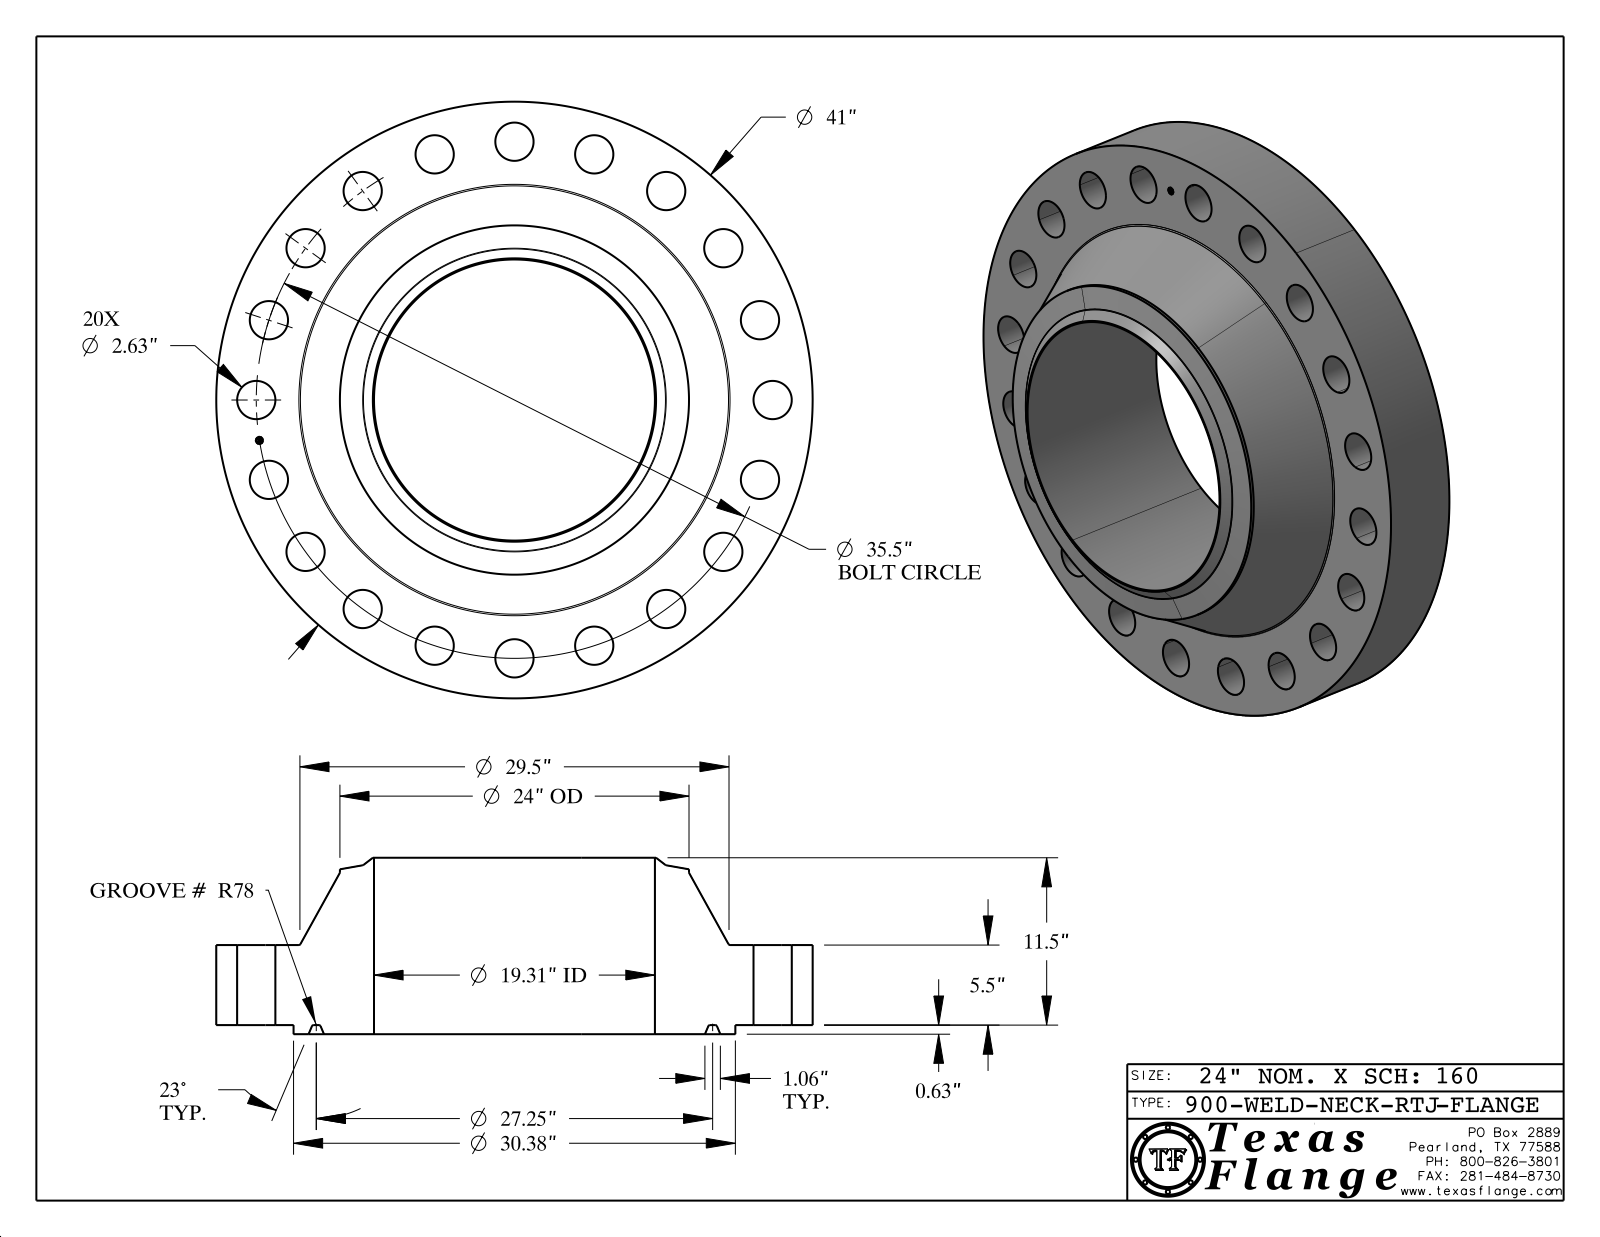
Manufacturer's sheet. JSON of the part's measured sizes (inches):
{"part_name": "900-WELD-NECK-RTJ", "step_written_by": "CATIA V5 STEP AP214 (AUTOMOTIVE_DESIGN)", "units": "inches", "bodies": {"solids": 1, "faces": 457, "planar": 371, "cylindrical": 68, "other": 18}, "overall_size": [41, 41, 12.125], "volume_in3": 6707, "surface_area_in2": 4594, "round_holes": [[2.63, 20], [0.495, 1], [19.312, 1]], "round_bosses_or_shafts": [[0.03, 8], [41, 1], [30.375, 1], [24, 1], [0.39, 1]], "face_to_face_distances": [5.5, 0.625, 6.125, 12.125, 11.5, 6, 6.11, 5.485, 0.015, 6.015], "hole_center_spacings": [17.75, 10.97, 28.72, 31.631, 16.117, 20.866, 25.102, 33.762]}
